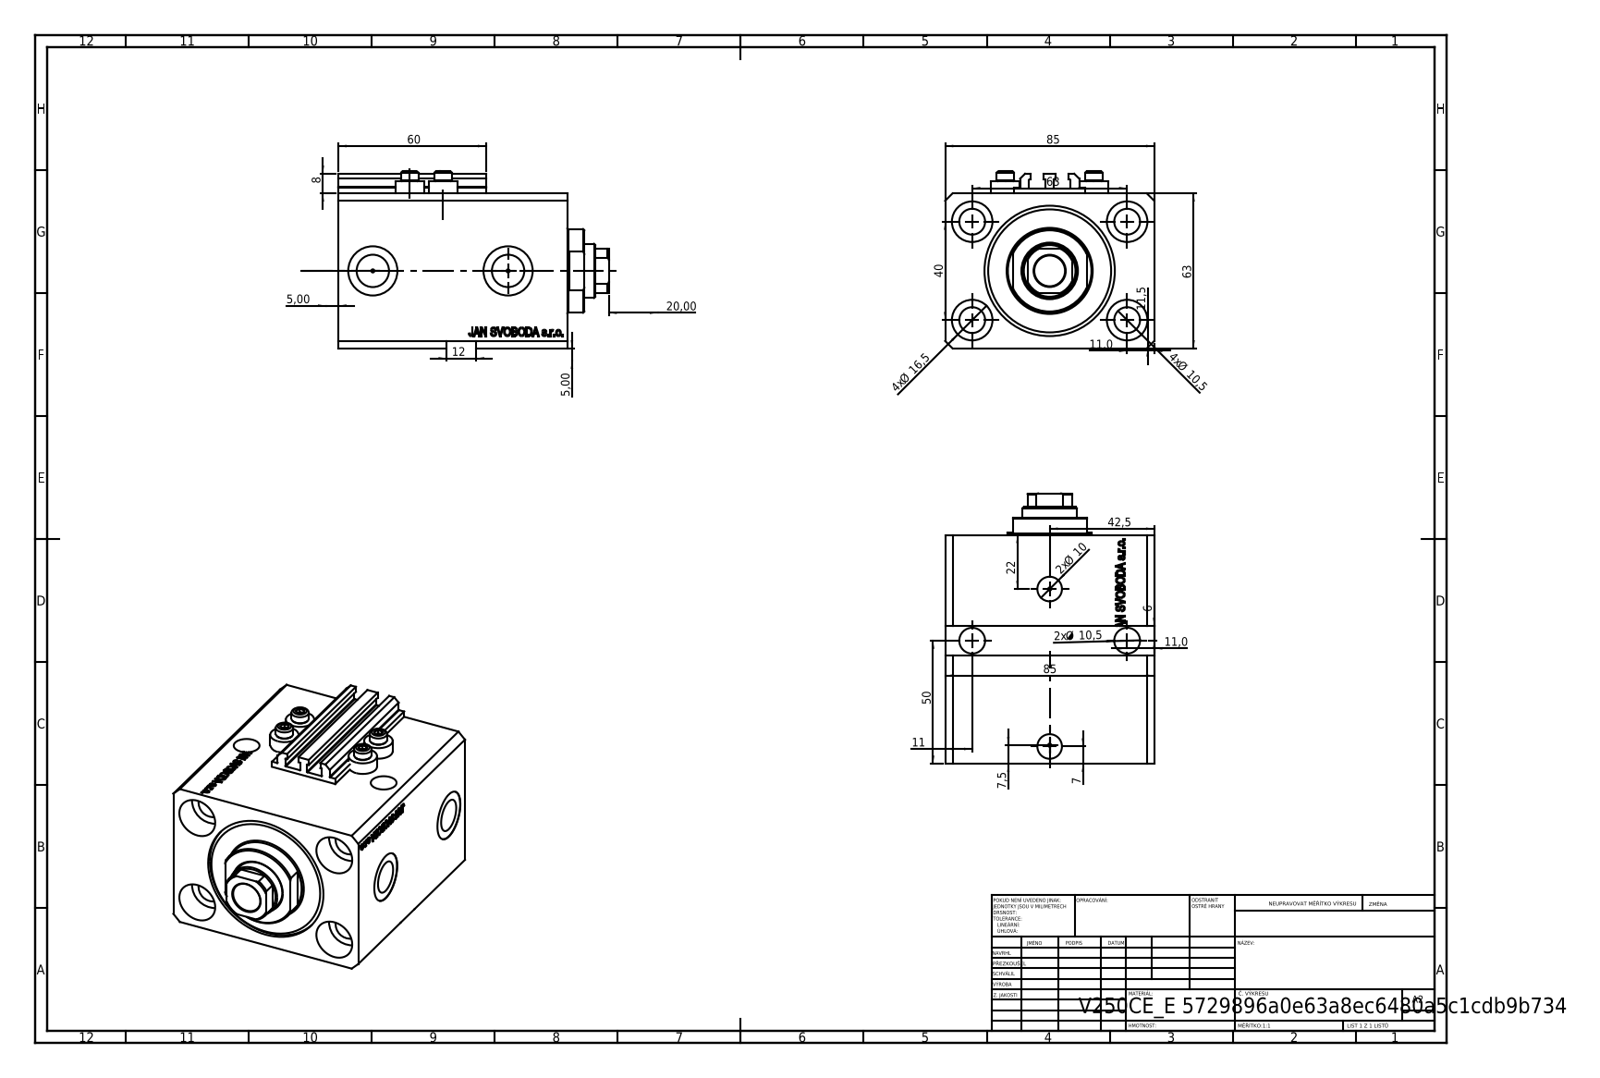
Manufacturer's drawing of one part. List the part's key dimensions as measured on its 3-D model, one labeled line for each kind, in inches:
Part name (STEP PRODUCT): V250CE_C_VCP; V250CE_VC_E; V250CE_E_Body; ALLEN BOLT V250CE
STEP written by: SolidWorks 2019 (CONFIG_CONTROL_DESIGN)
Units: inches
Bodies: 8 solids, 1103 faces (539 planar, 138 cylindrical, 426 other)
Overall size (bounding box): 4.327 × 3.346 × 2.835
Volume: 26.46 in³ · Surface area: 153.6 in²
Round holes (diameter × count): ⌀0.413 ×6, ⌀0.049 ×4, ⌀0.157 ×4, ⌀0.65 ×4, ⌀0.394 ×2, ⌀0.518 ×2, ⌀0.787 ×2, ⌀0.492 ×1, ⌀0.866 ×1, ⌀1.575 ×1, ⌀2.087 ×1
Round bosses / shafts (diameter × count): ⌀0.457 ×4, ⌀0.276 ×4, ⌀1.339 ×1
Partial cylindrical surfaces — rounded edges, fillets, slot ends (radius × count): R0.008 ×10, R0.413 ×1
Main face-to-face distances: 2.48, 3.346, 3.661, 2.594, 2.146, 1.067, 0.449, 3.213, 0.118, 2.559
Hole centre spacings: 1.469, 2.48, 0.535, 0.606, 0.983, 1.103, 1.119, 1.324
